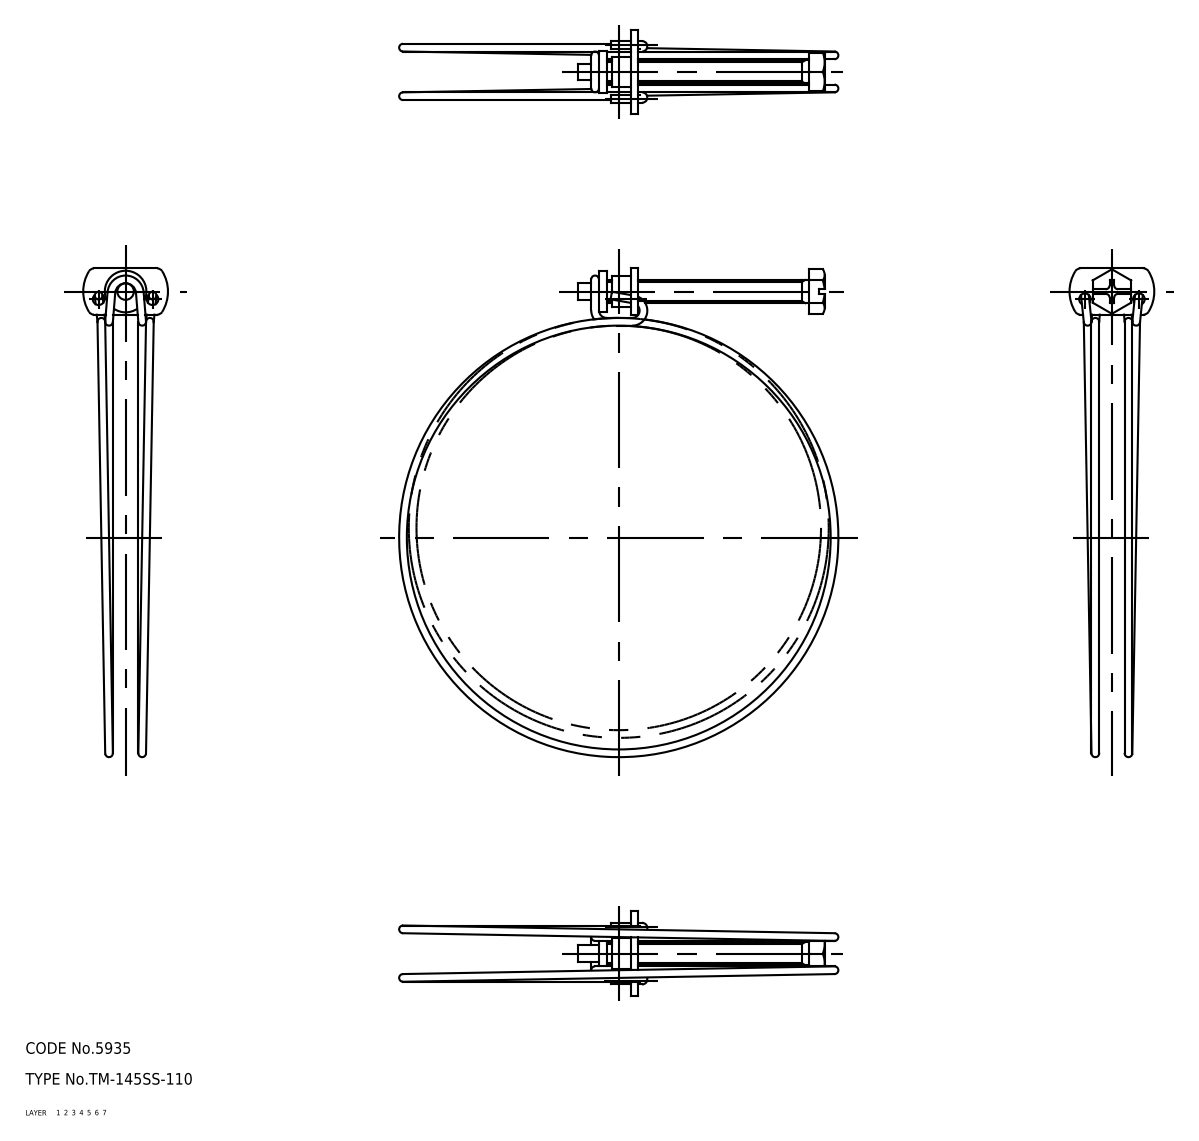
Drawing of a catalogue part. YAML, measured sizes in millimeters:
part_name: "screw; holder; band; TM_145SS_110_19045_36"
step_written_by: "CADfix (AUTOMOTIVE_DESIGN)"
units: millimeters
bodies: {solids: 3, faces: 90, planar: 0, cylindrical: 0, other: 90}
overall_size: [126.85, 114, 22]
volume: 4991
surface_area: 7306
